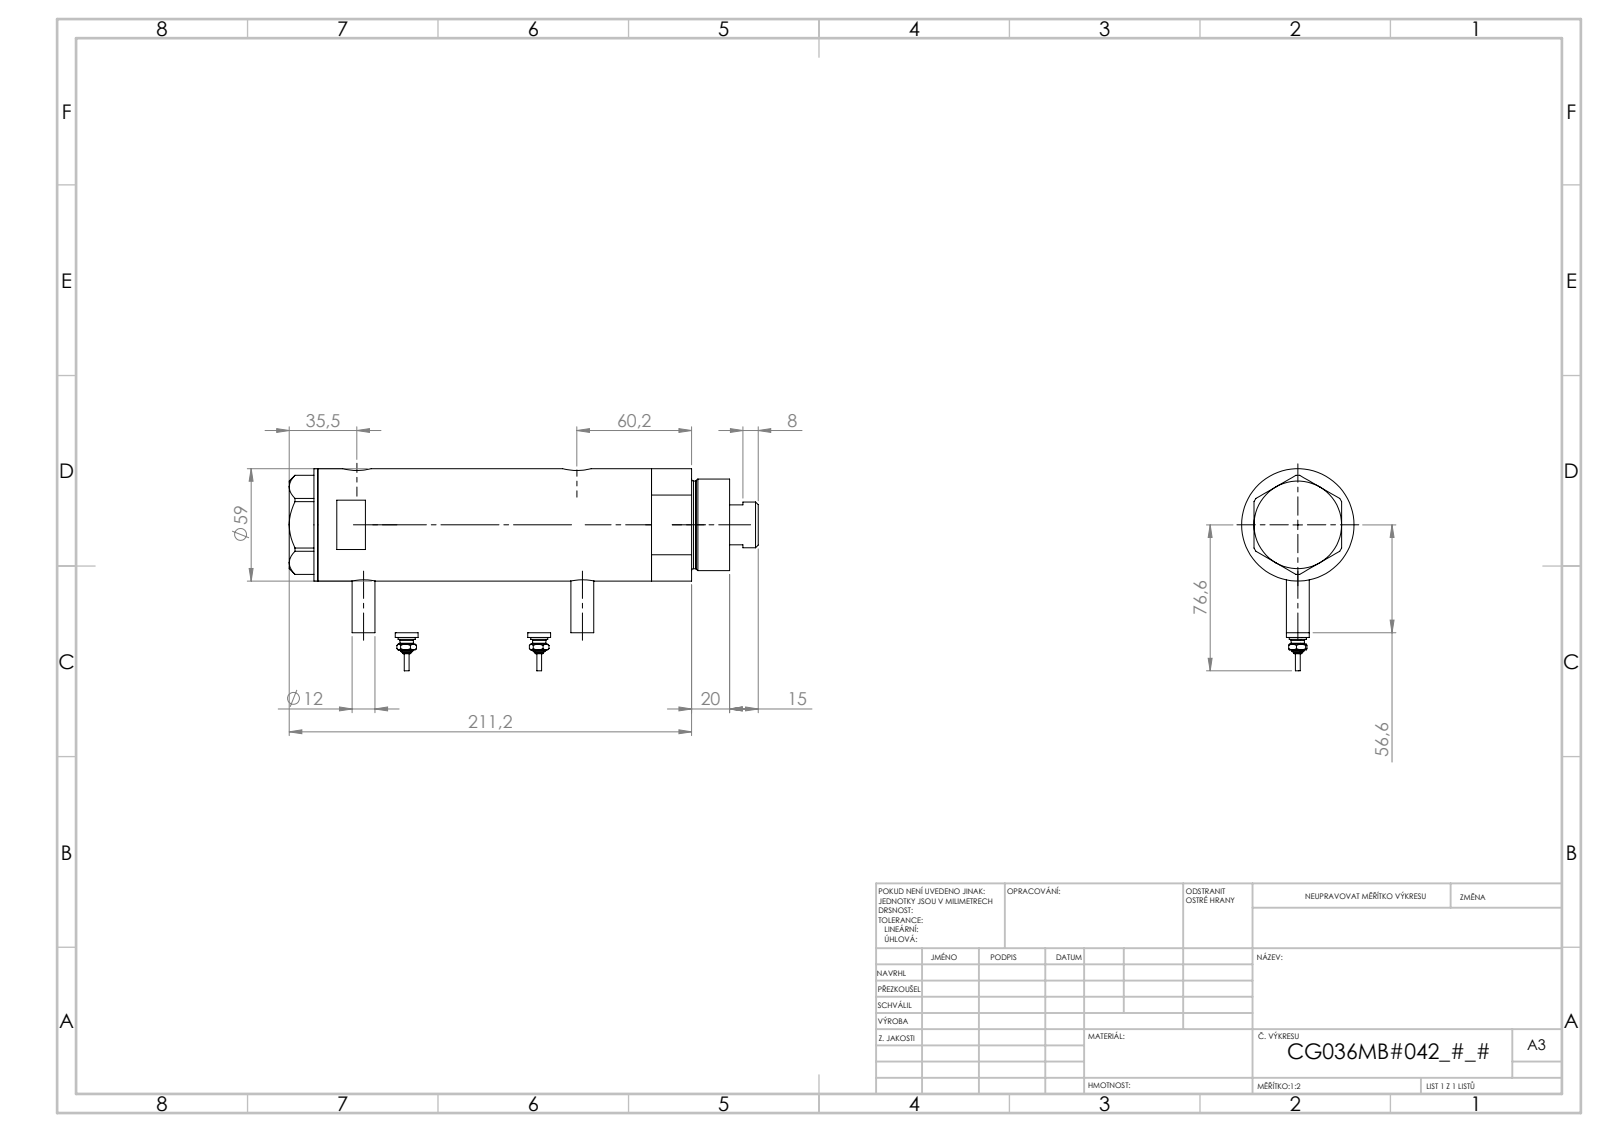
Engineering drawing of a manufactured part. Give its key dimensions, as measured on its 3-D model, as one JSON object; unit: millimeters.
{"part_name": "V270CG_MIDDLE; V270CG_SWITCH; V270CG_FRONT; V270CG_VC (+1 more)", "step_written_by": "SolidWorks 2019 (CONFIG_CONTROL_DESIGN)", "units": "millimeters", "bodies": {"solids": 6, "faces": 232, "planar": 81, "cylindrical": 77, "other": 74}, "overall_size": [205.42, 91.3, 59], "volume_mm3": 466691, "surface_area_mm2": 99673, "round_holes": [[5, 2], [9.73, 2], [12.5, 2], [15, 2], [8.5, 1], [25, 1], [26.5, 1], [36, 1], [40, 1], [52, 1]], "round_bosses_or_shafts": [[12, 4], [9, 2], [7, 2], [4.34, 2], [2.4, 2], [59, 1], [48, 1], [46, 1]], "face_to_face_distances": [23.5, 15, 38.5, 114.34, 99.34, 75.84, 190.42, 175.42, 151.92, 76.08], "hole_center_spacings": [2.9, 3.5, 74.15, 77.05, 77.65, 80.55, 2.89, 2.91]}
